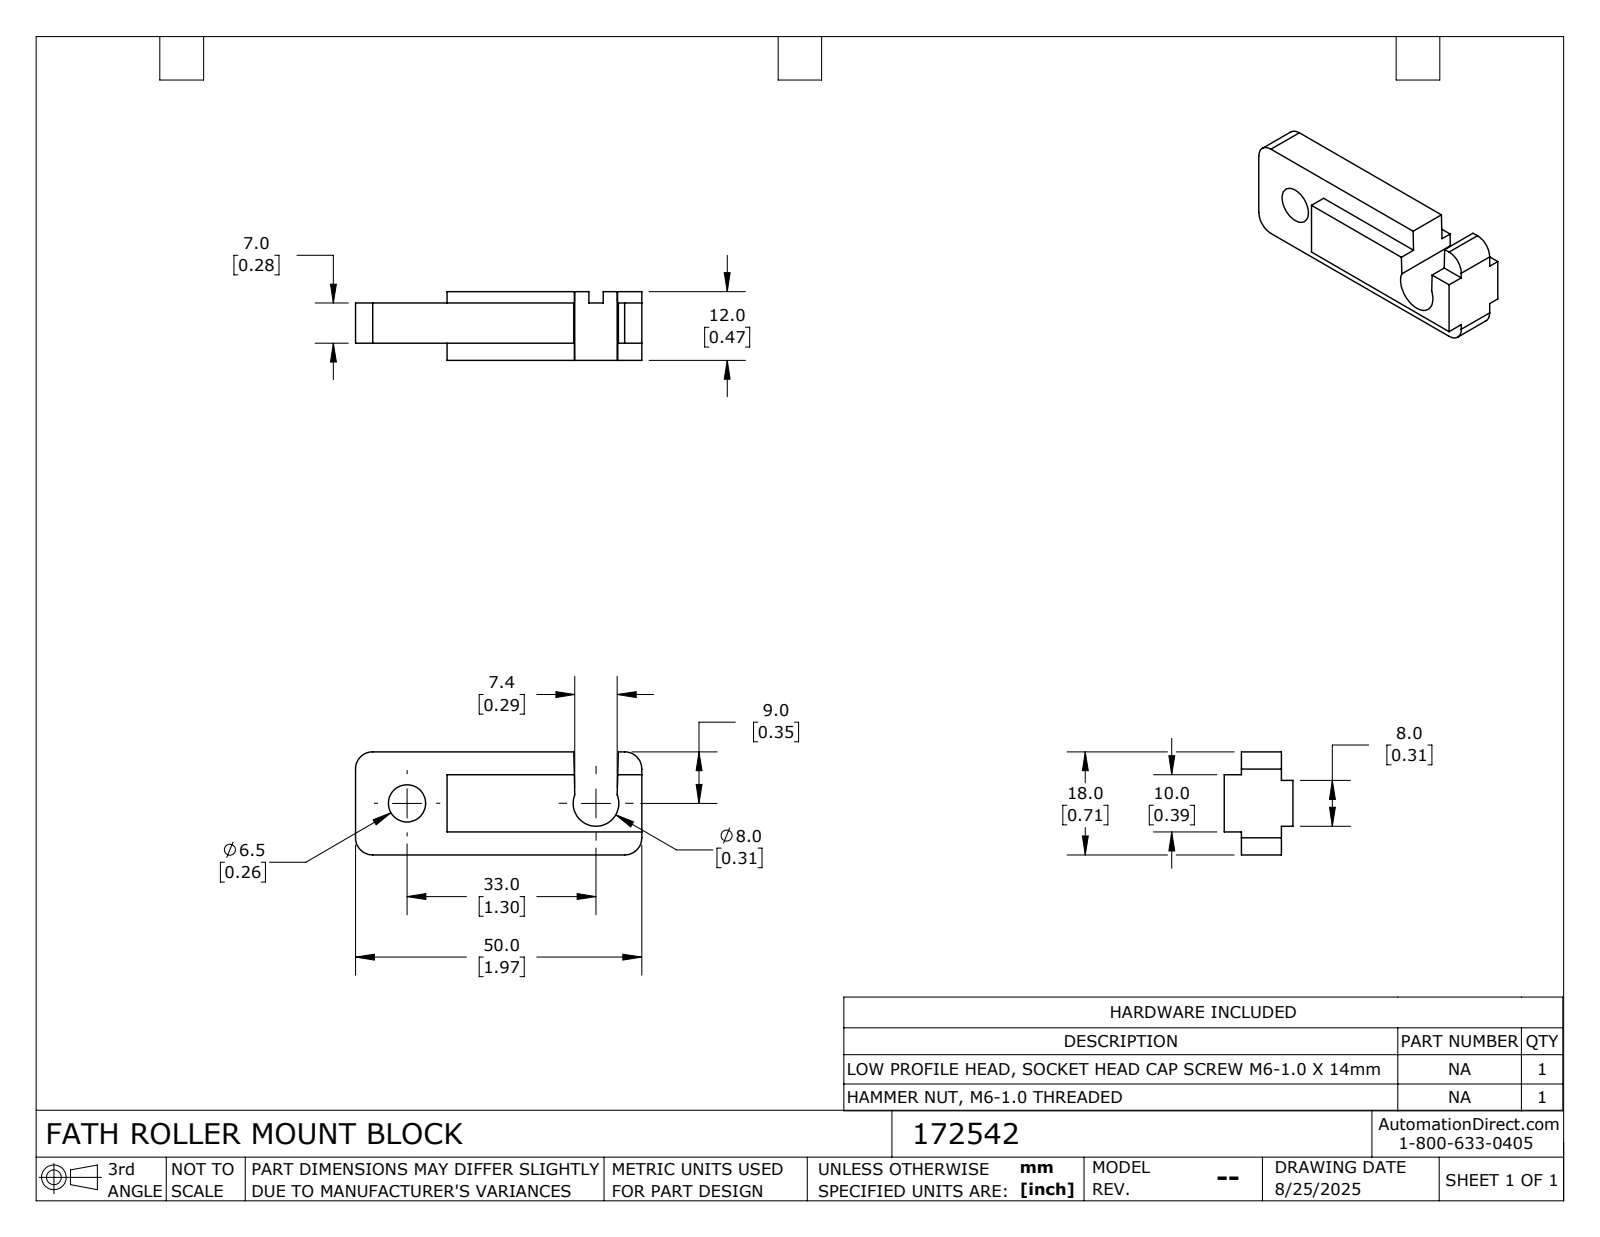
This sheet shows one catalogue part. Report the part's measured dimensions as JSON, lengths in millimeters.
{"part_name": "172542", "step_written_by": "SolidWorks 2024 (CONFIG_CONTROL_DESIGN)", "units": "millimeters", "bodies": {"solids": 1, "faces": 34, "planar": 25, "cylindrical": 9, "other": 0}, "overall_size": [50, 18, 12], "volume_mm3": 6622, "surface_area_mm2": 3243, "round_holes": [[6.5, 1]], "partial_cylinders_radius": [[3, 4], [3.99, 1]], "face_to_face_distances": [7, 10, 9, 3, 18, 2, 12, 4, 14, 5]}
